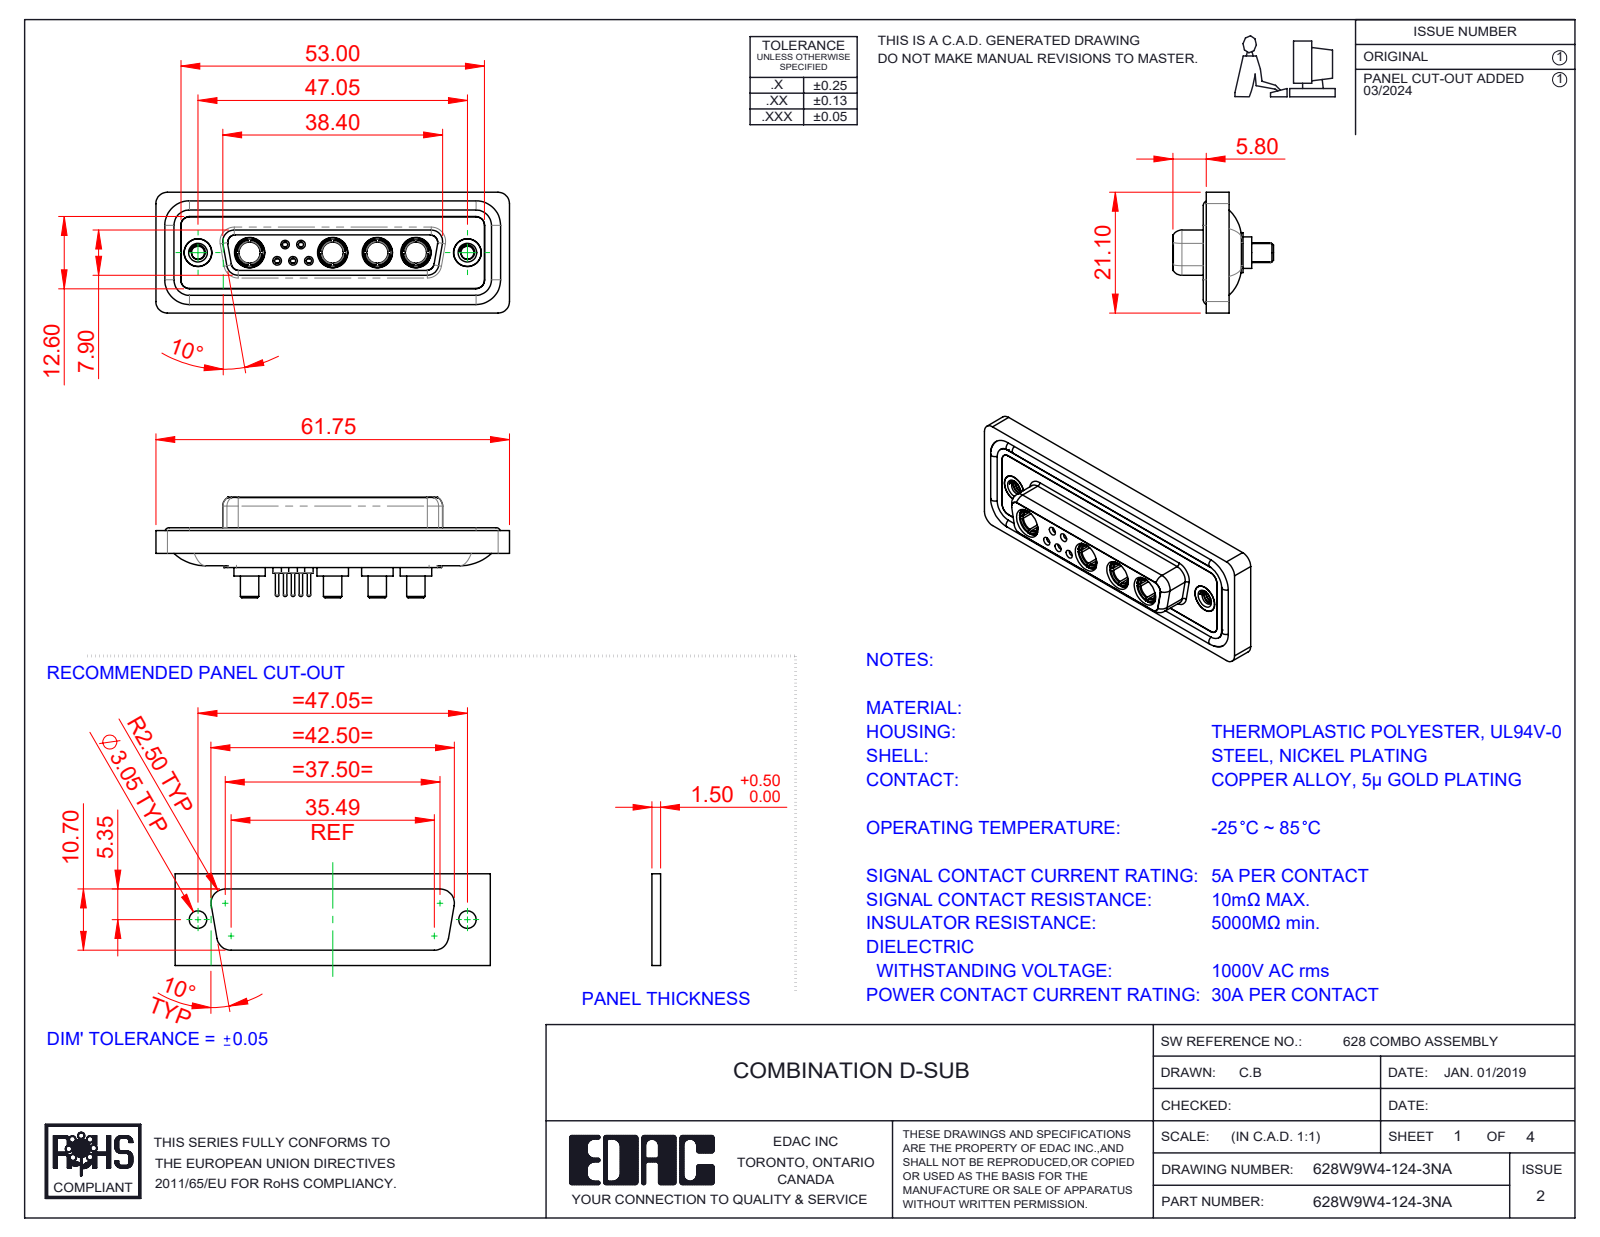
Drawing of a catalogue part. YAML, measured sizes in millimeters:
part_name: "628Combo Contact Row 1_24; Power Socket_30A S; 628Combo Housing_9W4; 628Combo Waterproof Housing_25 Contacts (+5 more)"
step_written_by: "SolidWorks 2023 (CONFIG_CONTROL_DESIGN)"
units: millimeters
bodies: {solids: 20, faces: 955, planar: 296, cylindrical: 377, other: 282}
overall_size: [61.75, 21.1, 17.55]
volume: 8253
surface_area: 13578
round_holes:
  - {diameter: 4.85, count: 6}
  - {diameter: 0.9, count: 5}
  - {diameter: 1.1, count: 5}
  - {diameter: 1.5, count: 5}
  - {diameter: 2, count: 5}
  - {diameter: 3.7, count: 4}
  - {diameter: 5.3, count: 4}
  - {diameter: 1.6, count: 3}
  - {diameter: 1.7, count: 2}
  - {diameter: 2.26, count: 2}
  - {diameter: 4, count: 2}
  - {diameter: 4.05, count: 2}
round_bosses_or_shafts:
  - {diameter: 1.6, count: 6}
  - {diameter: 2.2, count: 5}
  - {diameter: 0.6, count: 5}
  - {diameter: 5.5, count: 4}
  - {diameter: 5.2, count: 4}
  - {diameter: 4.96, count: 4}
  - {diameter: 4.75, count: 4}
  - {diameter: 3.75, count: 4}
partial_cylinders:
  - {radius: 1.5, count: 22}
  - {radius: 2, count: 18}
  - {radius: 1.35, count: 8}
  - {radius: 1.6, count: 8}
  - {radius: 0.25, count: 4}
  - {radius: 0.5, count: 4}
  - {radius: 0.6, count: 4}
  - {radius: 0.65, count: 4}
face_to_face_distances: [0.4, 1.8, 7.45, 5.65, 0.5, 7.05, 6.6, 1.6, 1.1, 2.9]
hole_center_spacings: [3.16, 2.77, 5.03, 2.76, 4.4, 5.02, 5.54, 5.73]
